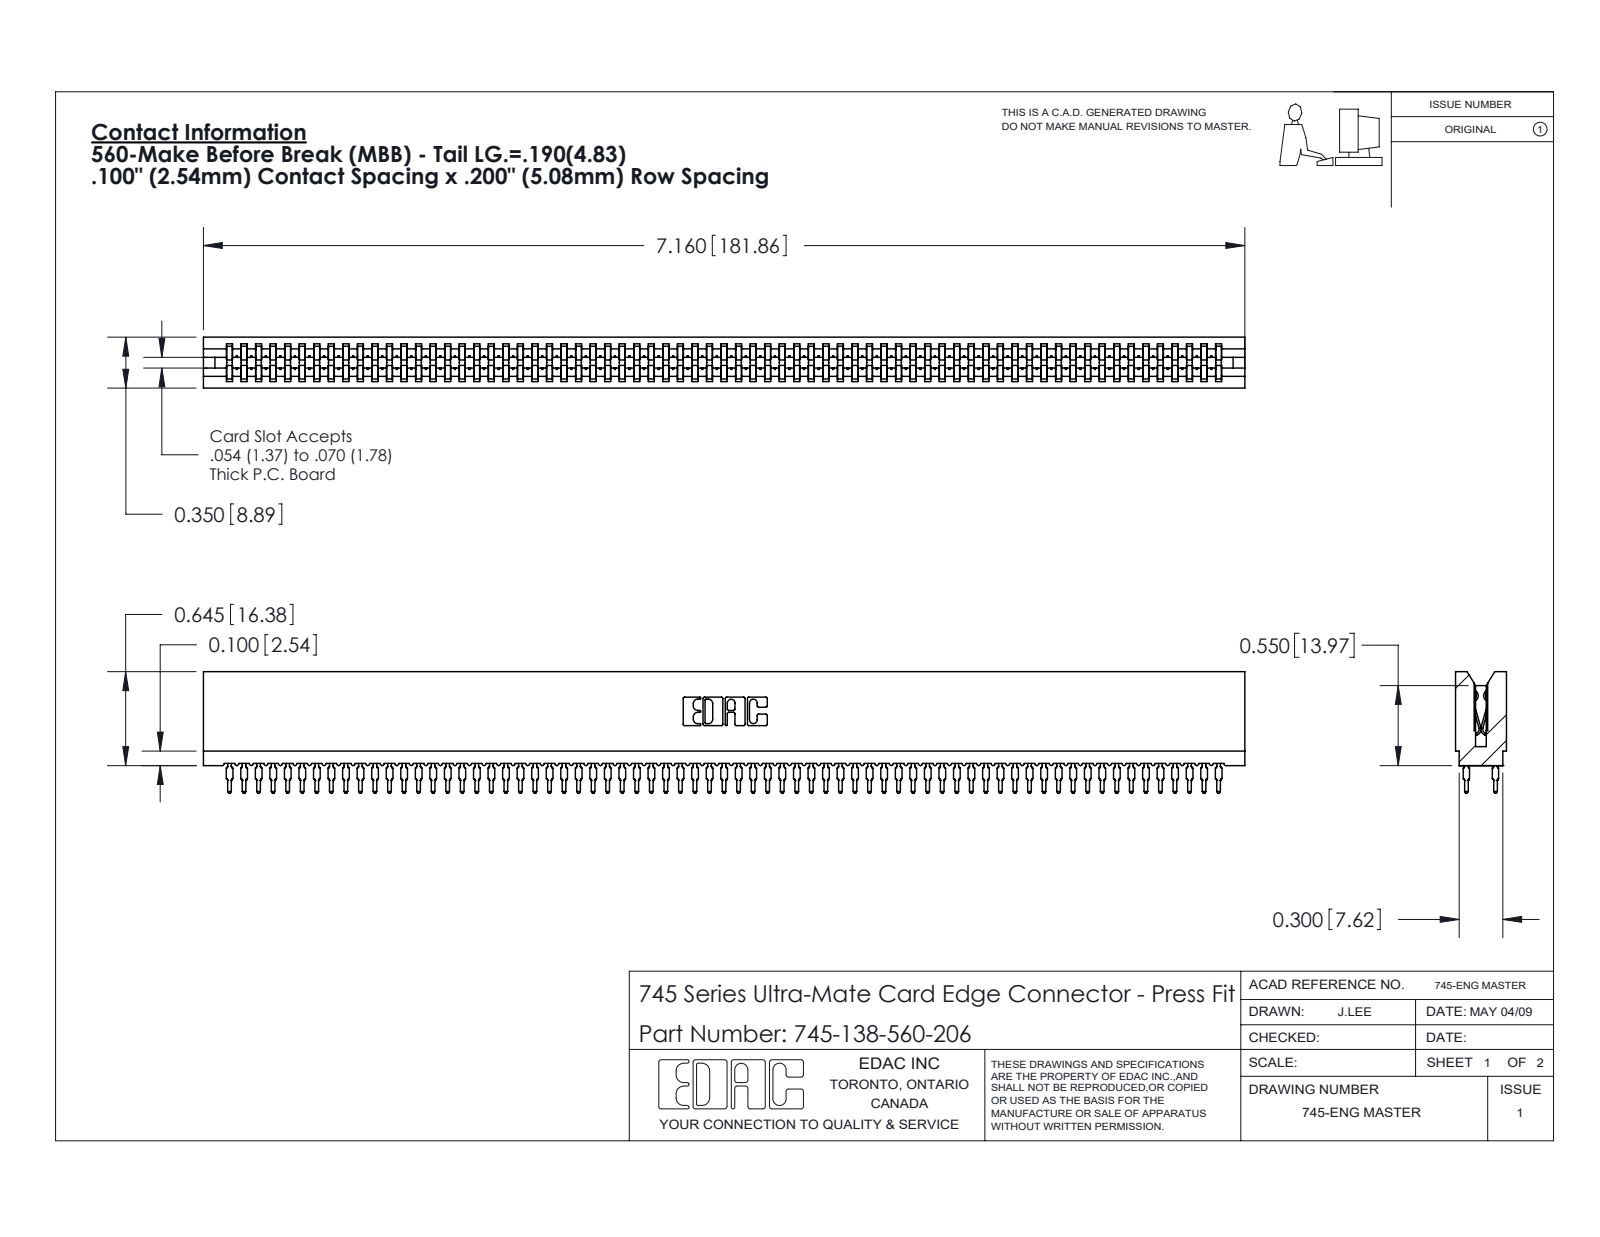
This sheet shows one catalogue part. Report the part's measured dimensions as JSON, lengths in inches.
{"part_name": "745-138-560-206; 745-292-001_560; 745 Part_Insulator Option - 06", "step_written_by": "SolidWorks 2020 (CONFIG_CONTROL_DESIGN)", "units": "inches", "bodies": {"solids": 139, "faces": 13689, "planar": 7094, "cylindrical": 3007, "other": 3588}, "overall_size": [7.16, 0.836, 0.35], "volume_in3": 1.019, "surface_area_in2": 57.02, "partial_cylinders_radius": [[0.021, 276], [0.015, 138], [0.01, 22], [0.005, 8], [0.011, 8], [0.007, 6], [0.031, 6], [0.026, 3]], "face_to_face_distances": [0.35, 0.063, 0.287, 0.045, 0.305, 0.018, 0.243, 0.138, 0.212, 0.093]}
